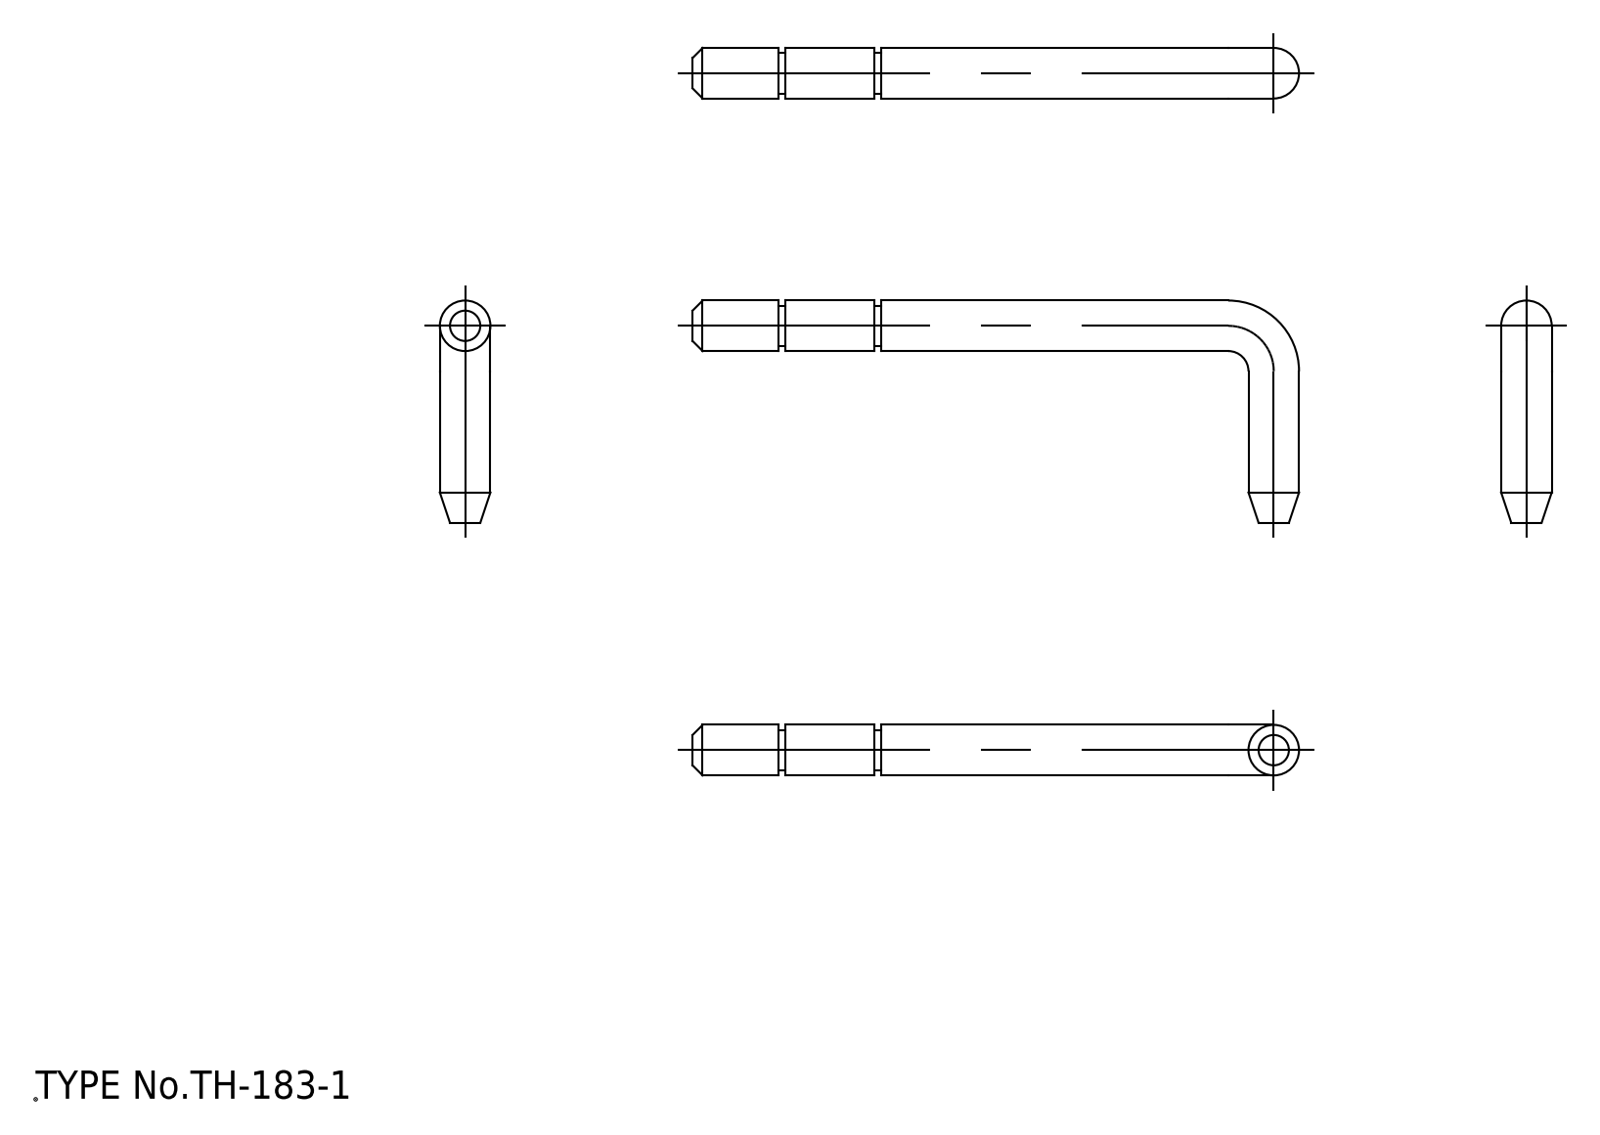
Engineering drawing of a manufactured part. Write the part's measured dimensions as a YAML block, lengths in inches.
step_written_by: "spGate 19.8.4 (****-****-****-****) (AUTOMOTIVE_DESIGN)"
units: inches
bodies: {solids: 1, faces: 24, planar: 6, cylindrical: 12, other: 6}
overall_size: [2.362, 0.866, 0.197]
volume: 0.088
surface_area: 1.879
round_bosses_or_shafts:
  - {diameter: 0.197, count: 2}
  - {diameter: 0.157, count: 1}
face_to_face_distances: [0.028, 0.374, 0.709, 0.335, 0.362, 0.736, 0.402, 0.346]
